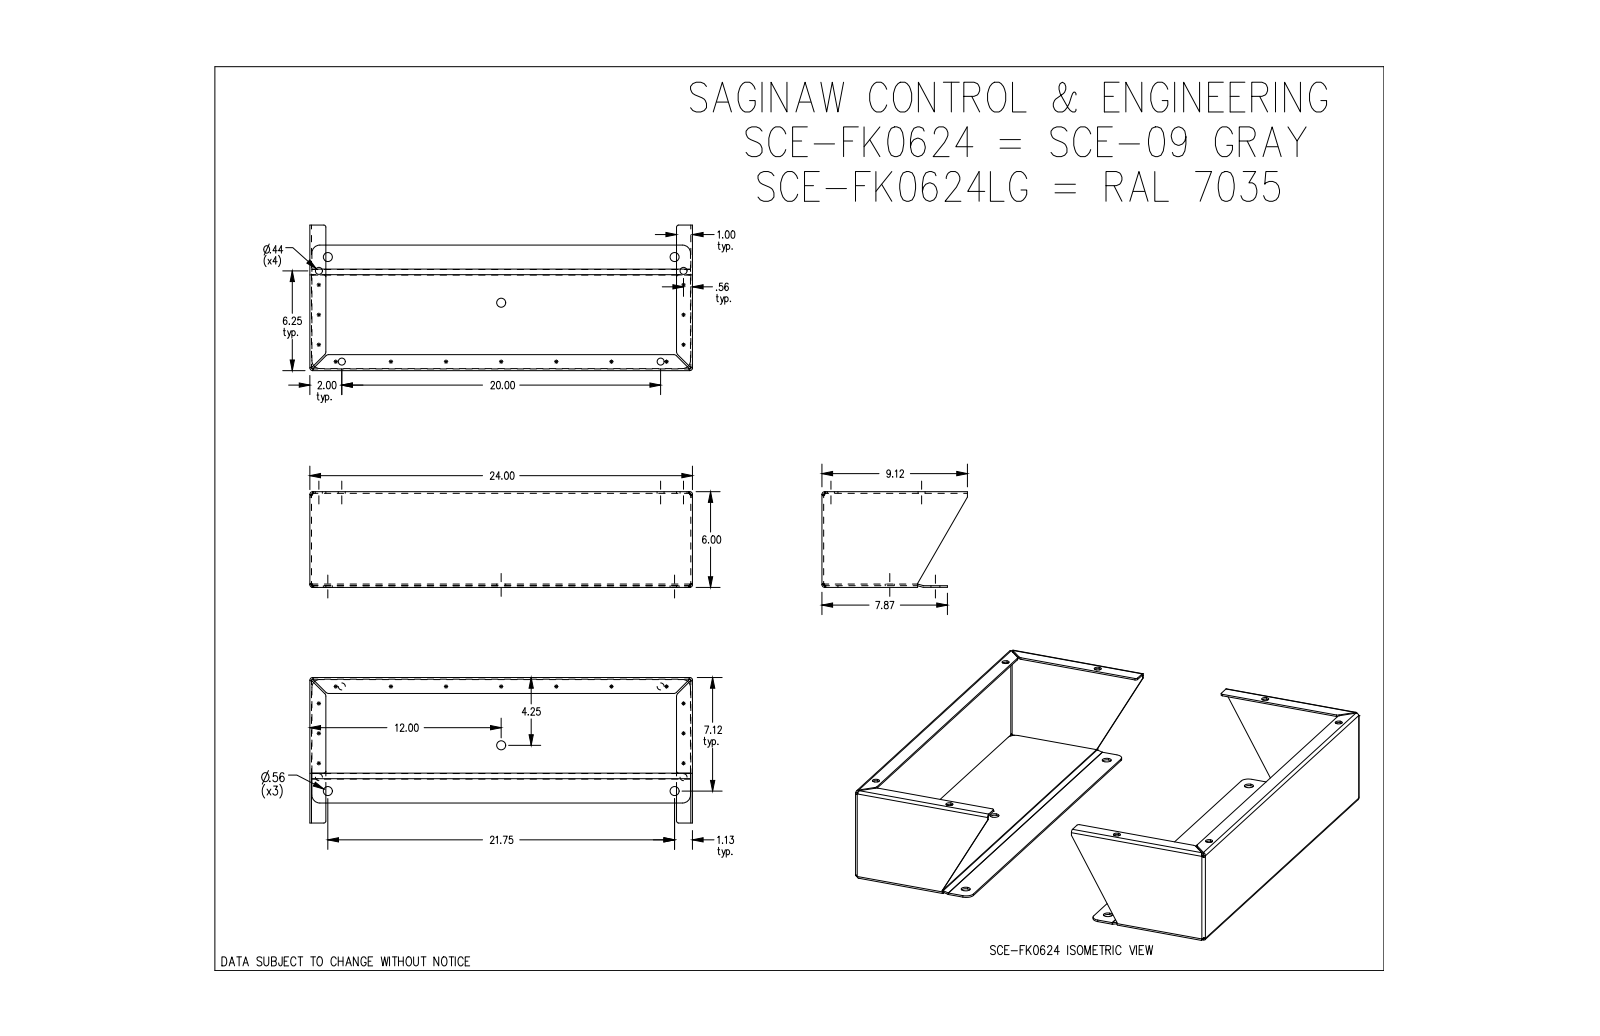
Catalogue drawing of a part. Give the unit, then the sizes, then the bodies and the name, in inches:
Units: inches
Overall size (bounding box): 24 × 24 × 6
Round holes (diameter × count): ⌀0.437 ×8, ⌀0.563 ×6
Partial cylindrical surfaces — rounded edges, fillets, slot ends (radius × count): R0.166 ×16, R0.062 ×10, R0.063 ×10, R0.125 ×8, R0.22 ×8, R0.5 ×8
Main face-to-face distances: 0.104, 23.896, 24, 23.792, 0.101, 5.893, 5.792, 5.896, 0.205, 5.997
Hole centre spacings: 1.035, 5.866, 6.614, 10.646, 10.659, 11.611, 16.343, 17.247
Volume: 99.31 in³ · Surface area: 1 945 in²
Bodies: 4 solids, 214 faces (96 planar, 86 cylindrical, 32 other)
Part name (STEP PRODUCT): SCE-FK0624
STEP written by: SolidWorks 2019 (CONFIG_CONTROL_DESIGN)
